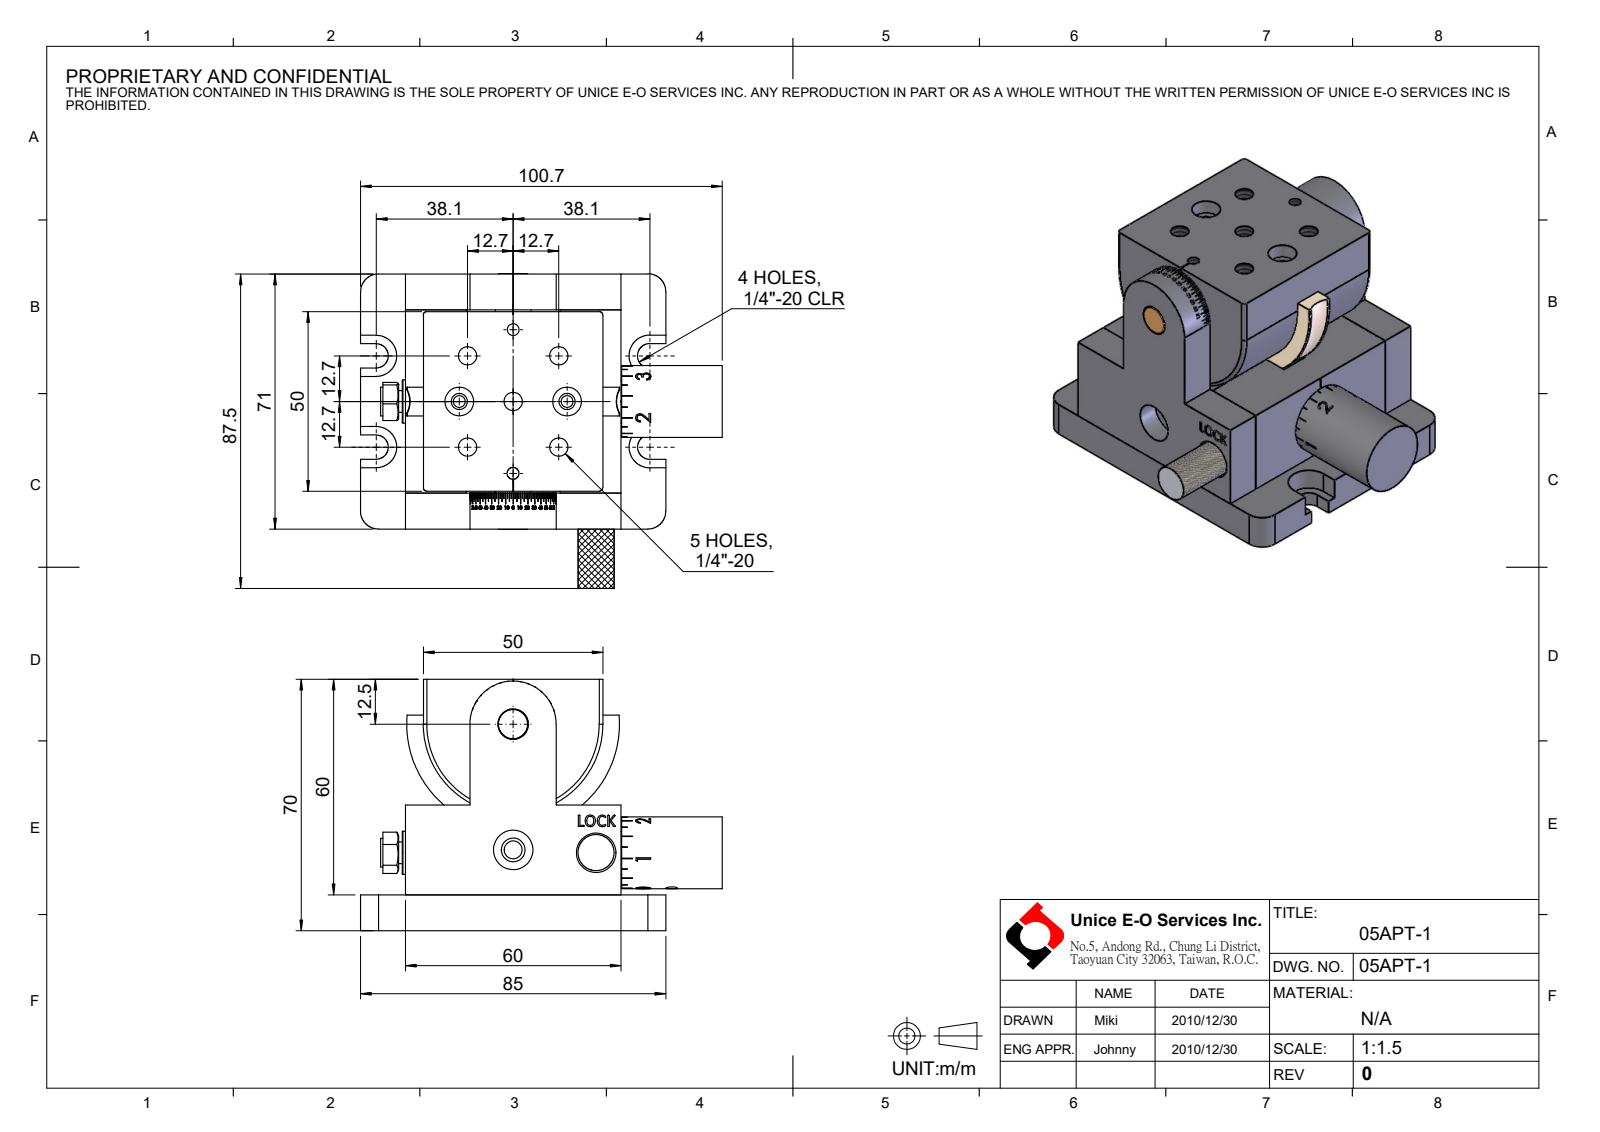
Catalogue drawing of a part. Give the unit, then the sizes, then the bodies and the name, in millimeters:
Units: millimetres
Overall size (bounding box): 100.7 × 87.6 × 70
Round holes (diameter × count): ⌀5 ×8, ⌀11 ×8, ⌀3.3 ×5, ⌀5.11 ×5, ⌀6.6 ×5, ⌀8 ×3, ⌀4.5 ×2, ⌀10 ×2, ⌀12 ×2, ⌀4.2 ×1, ⌀6 ×1, ⌀6.65 ×1
Round bosses / shafts (diameter × count): ⌀9 ×2, ⌀20 ×1, ⌀15.6 ×1, ⌀10 ×1, ⌀8 ×1, ⌀7.5 ×1, ⌀5 ×1, ⌀4 ×1
Partial cylindrical surfaces — rounded edges, fillets, slot ends (radius × count): R1 ×4, R3.38 ×4, R3.5 ×4, R5 ×4, R5.75 ×4, R7.34 ×1, R9.98 ×1, R11.98 ×1
Main face-to-face distances: 10, 61, 31.5, 39.5, 21.5, 29.5, 60, 35, 51, 10.5
Hole centre spacings: 33.5, 20, 40, 10.32, 12.91, 14.65, 15, 17.96
Volume: 252 628 mm³ · Surface area: 78 347 mm²
Bodies: 19 solids, 2289 faces (1029 planar, 306 cylindrical, 954 other)
Part name (STEP PRODUCT): 05APT-1
STEP written by: SolidWorks 2016 (CONFIG_CONTROL_DESIGN)
